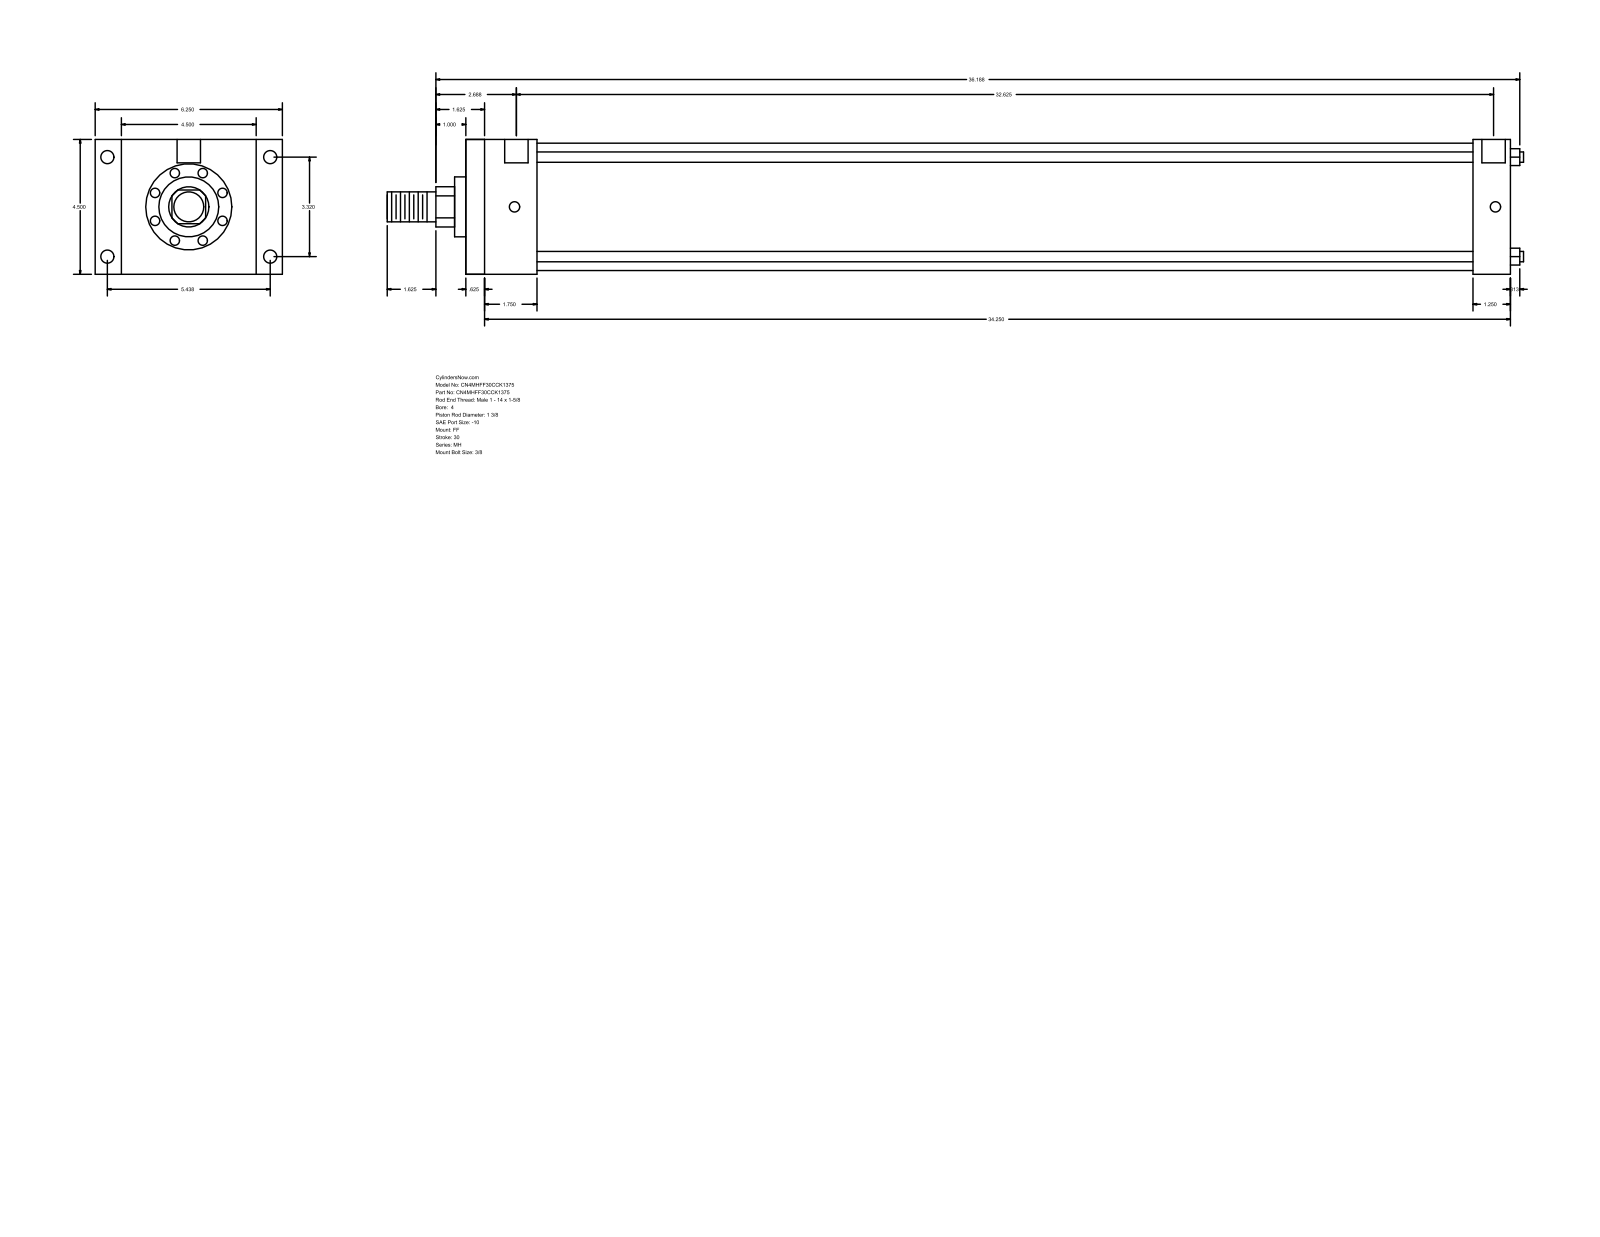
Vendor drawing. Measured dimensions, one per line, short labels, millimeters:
name: MH_FF__0400_1.375
written by: GSSL Pune (CONFIG_CONTROL_DESIGN)
unit: mm
bodies: 0 solids, 92 faces (64 planar, 28 cylindrical, 0 other)
size: 963.61 × 158.75 × 114.3
holes: 4× ⌀8.73, 4× ⌀11.13, 2× ⌀19.84
bosses: 4× ⌀8.76, 1× ⌀107.95, 1× ⌀50.8, 1× ⌀34.92, 1× ⌀25.4
rounds: 1× R17.06
face distances: 114.3, 885.83, 15.87, 869.96, 60.32, 44.45, 825.51, 854.08, 838.21, 793.76
hole spacings: 84.32, 138.12, 161.82, 831.85, 1.58, 1.59, 828.68, 830.26
